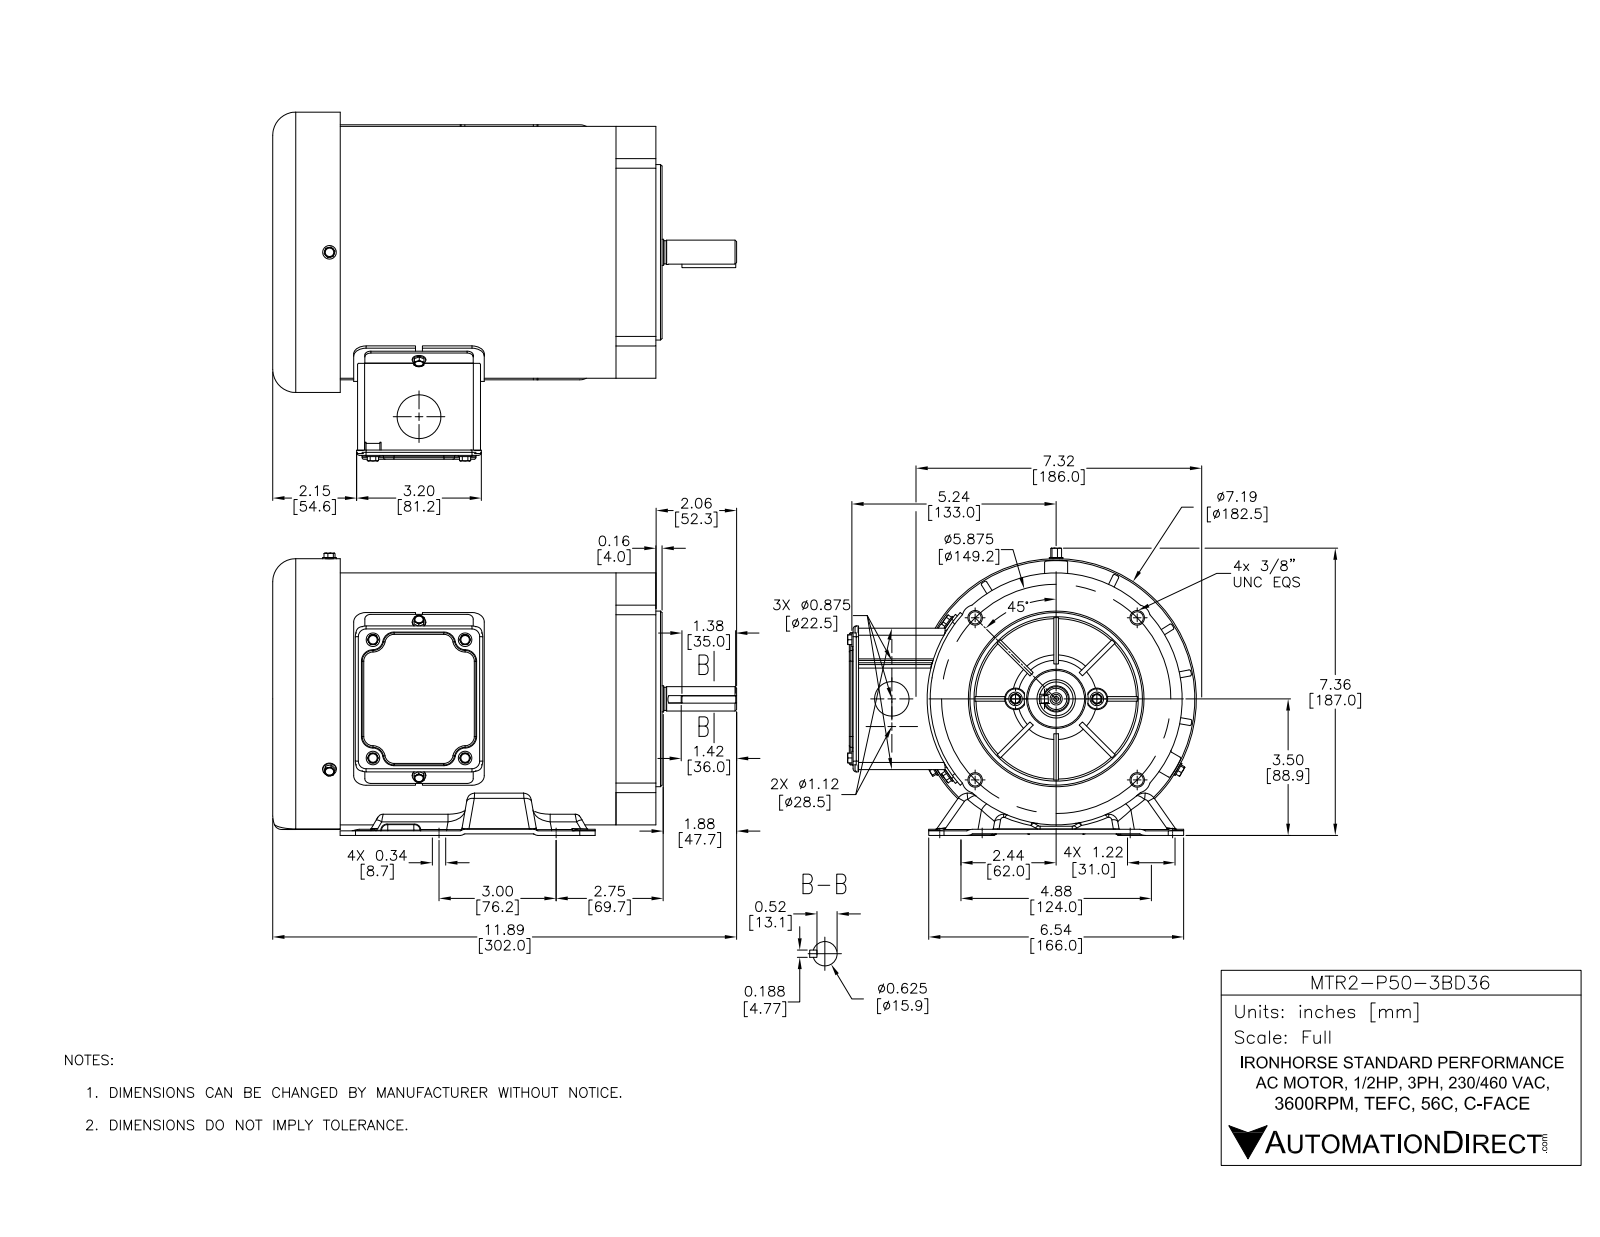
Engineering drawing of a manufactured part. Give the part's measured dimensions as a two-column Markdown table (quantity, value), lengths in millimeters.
| quantity | value |
| --- | --- |
| part name | MTR2-P50-3BD36 |
| STEP written by | SolidWorks 2016 (AUTOMOTIVE_DESIGN) |
| units | millimeters |
| bodies | 37 solids, 2761 faces (763 planar, 888 cylindrical, 1110 other) |
| overall size | 295.5 × 227 × 183.7 |
| volume | 795 600 mm³ |
| surface area | 629 900 mm² |
| round holes (diameter × count) | 5 × 12, 5.6 × 11, 7 × 8, 5.5 × 6, 8.7 × 6, 3.5 × 5, 3.8 × 4, 4.5 × 4, 8 × 4, 1.7 × 2, 3.4 × 2, 13 × 2 |
| round bosses / shafts (diameter × count) | 4.2 × 11, 8.8 × 7, 6.4 × 6, 8.8 × 4, 182.5 × 1, 164 × 1, 114.3 × 1, 24 × 1 |
| partial cylindrical surfaces (radius × count) | 3 × 121, 1 × 38, 0.5 × 32, 4 × 32, 3.5 × 26, 7 × 19, 4.4 × 12, 5 × 12 |
| main face-to-face distances | 3, 1, 1.6, 213, 26, 29, 242, 243, 90.4, 2 |
| hole center spacings | 107.2, 77, 2.4, 58.9, 61.2, 74.6, 75.7, 95.2 |
